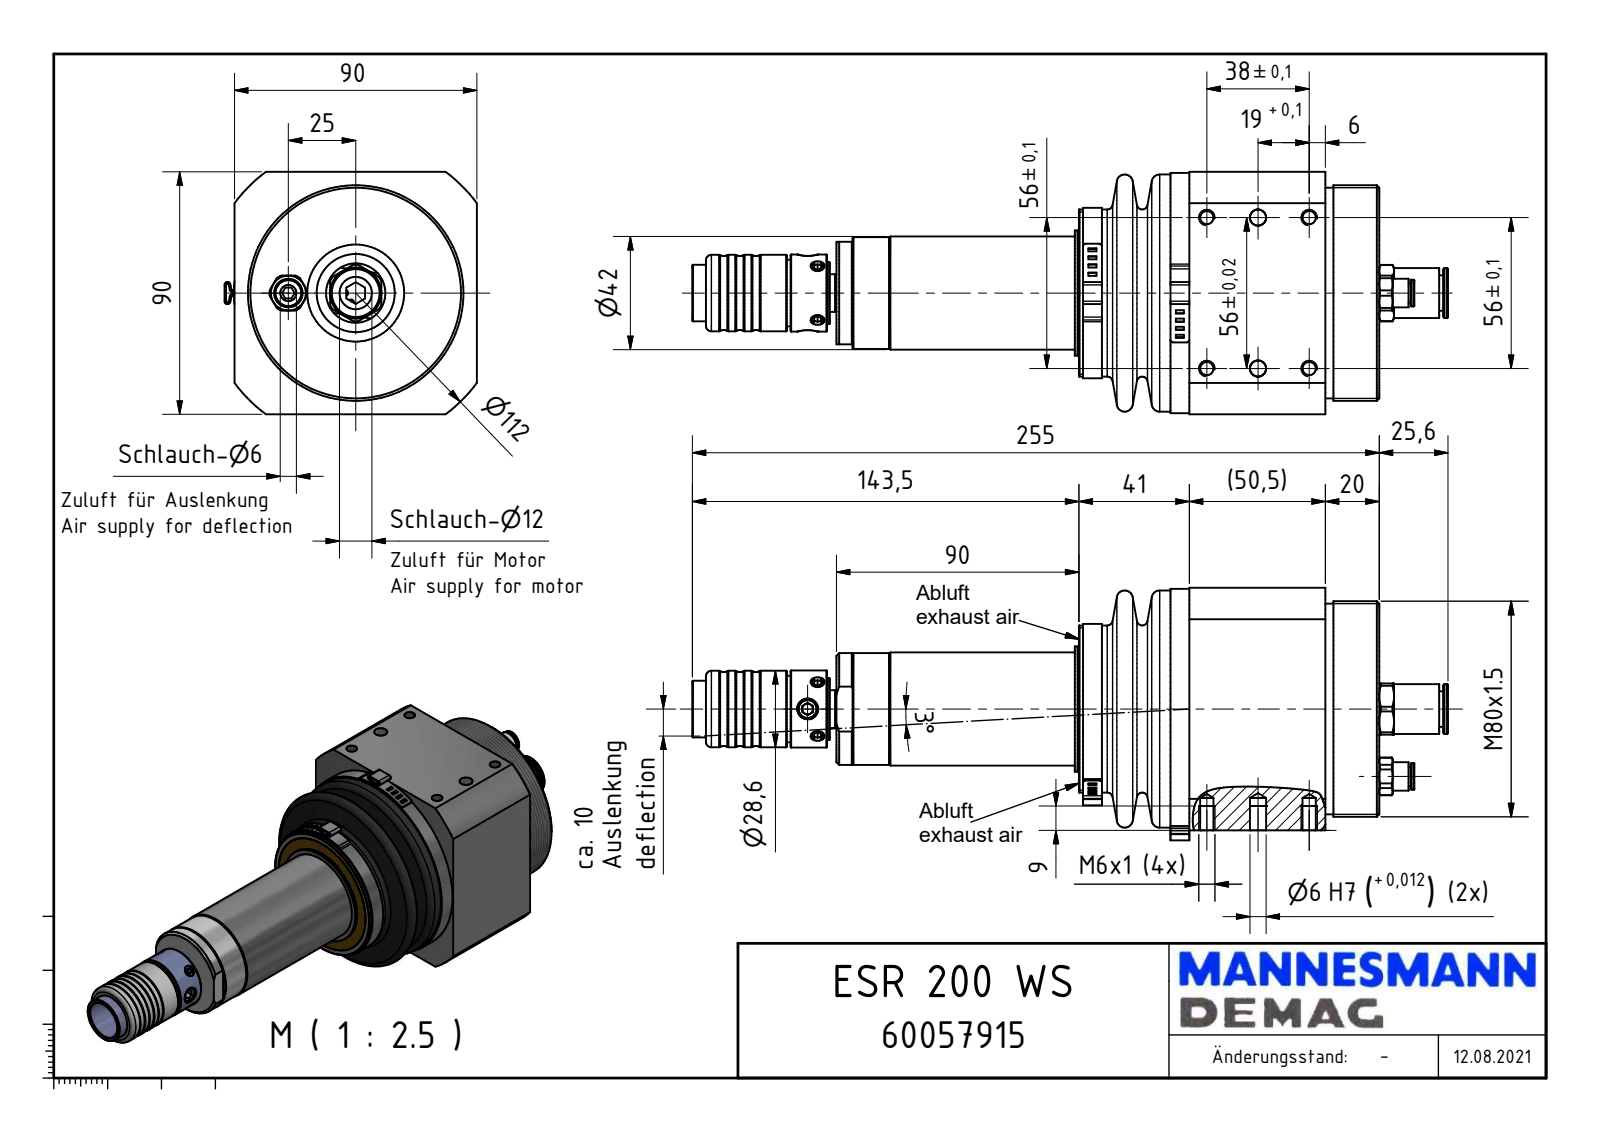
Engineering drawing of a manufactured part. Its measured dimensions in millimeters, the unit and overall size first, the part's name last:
Units: millimetres
Overall size (bounding box): 280.55 × 90 × 90
Round holes (diameter × count): ⌀4.92 ×4, ⌀6 ×3, ⌀6 ×2, ⌀2.5 ×1, ⌀4 ×1, ⌀6.65 ×1, ⌀8.57 ×1, ⌀9 ×1, ⌀9.75 ×1, ⌀12 ×1, ⌀14 ×1, ⌀16 ×1
Round bosses / shafts (diameter × count): ⌀88 ×1, ⌀80 ×1, ⌀78.18 ×1, ⌀62 ×1, ⌀60 ×1, ⌀46.5 ×1, ⌀46 ×1, ⌀42 ×1
Partial cylindrical surfaces — rounded edges, fillets, slot ends (radius × count): R1.4 ×2, R2.07 ×2, R2.5 ×2, R2 ×1, R7 ×1, R8.95 ×1, R13.32 ×1, R28.56 ×1
Main face-to-face distances: 90, 70.5, 20, 50.5, 111.5, 181.5, 201.5, 41, 91.5, 131
Hole centre spacings: 19, 59.14, 56, 28.04, 33.02, 34.7, 38, 67.68
Volume: 772 225 mm³ · Surface area: 101 125 mm²
Bodies: 1 solid, 343 faces (127 planar, 121 cylindrical, 95 other)
Part name (STEP PRODUCT): ESR 200 WS_60057915
STEP written by: Autodesk Inventor 2018 (AUTOMOTIVE_DESIGN)
